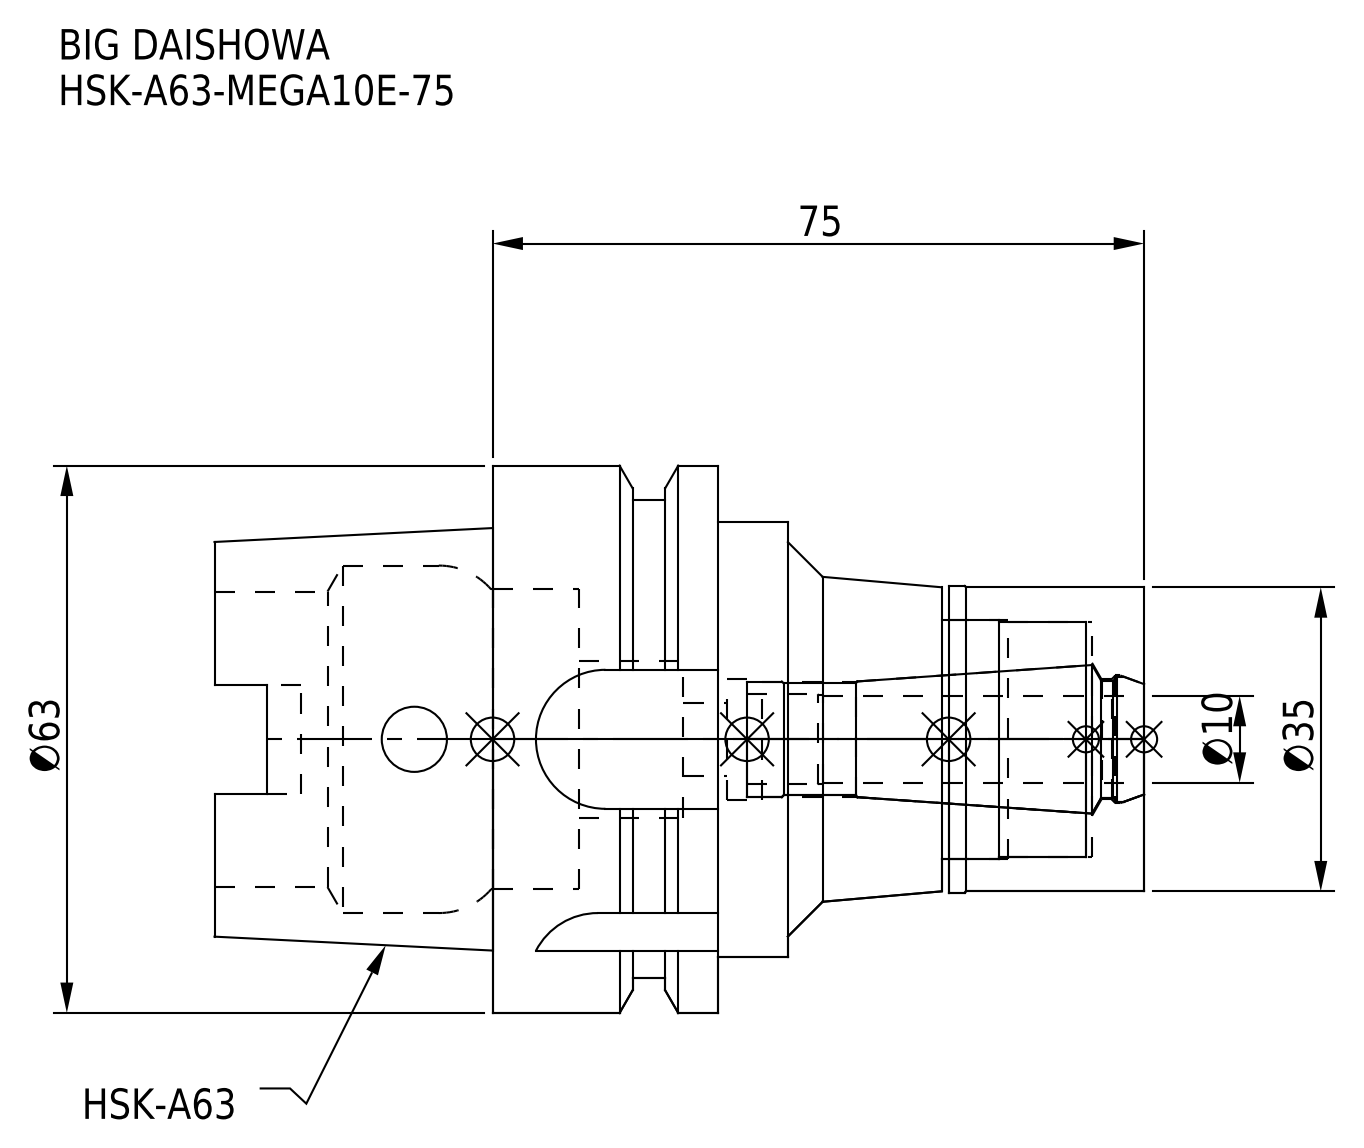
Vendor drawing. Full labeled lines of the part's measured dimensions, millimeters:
Part name (STEP PRODUCT): HSK-A63-MEGA10E-75-100-FreeParts; MEN10_1.stp; HSK-A63-MEGA10E-75-100.stp; DXF_TEMP_ASSY_ASM_4_ASM.stp (+3 more)
STEP written by: SolidWorks 2019 (CONFIG_CONTROL_DESIGN)
Units: millimetres
Bodies: 2 solids, 126 faces (44 planar, 54 cylindrical, 28 other)
Overall size (bounding box): 107 × 63 × 63
Volume: 130 735 mm³ · Surface area: 34 294 mm²
Round holes (diameter × count): ⌀7.5 ×1, ⌀8.39 ×1, ⌀8.4 ×1, ⌀13.3 ×1, ⌀13.8 ×1, ⌀13.9 ×1, ⌀14.7 ×1, ⌀18 ×1, ⌀27 ×1, ⌀27.5 ×1, ⌀34 ×1, ⌀34.5 ×1
Round bosses / shafts (diameter × count): ⌀63 ×1, ⌀55 ×1, ⌀50 ×1, ⌀35.3 ×1, ⌀35 ×1
Partial cylindrical surfaces — rounded edges, fillets, slot ends (radius × count): R2.8 ×2, R2.88 ×2, R8 ×2, R9 ×1
Main face-to-face distances: 26, 49, 75, 65.05, 16.05, 9.95, 107, 58, 41.95, 32
